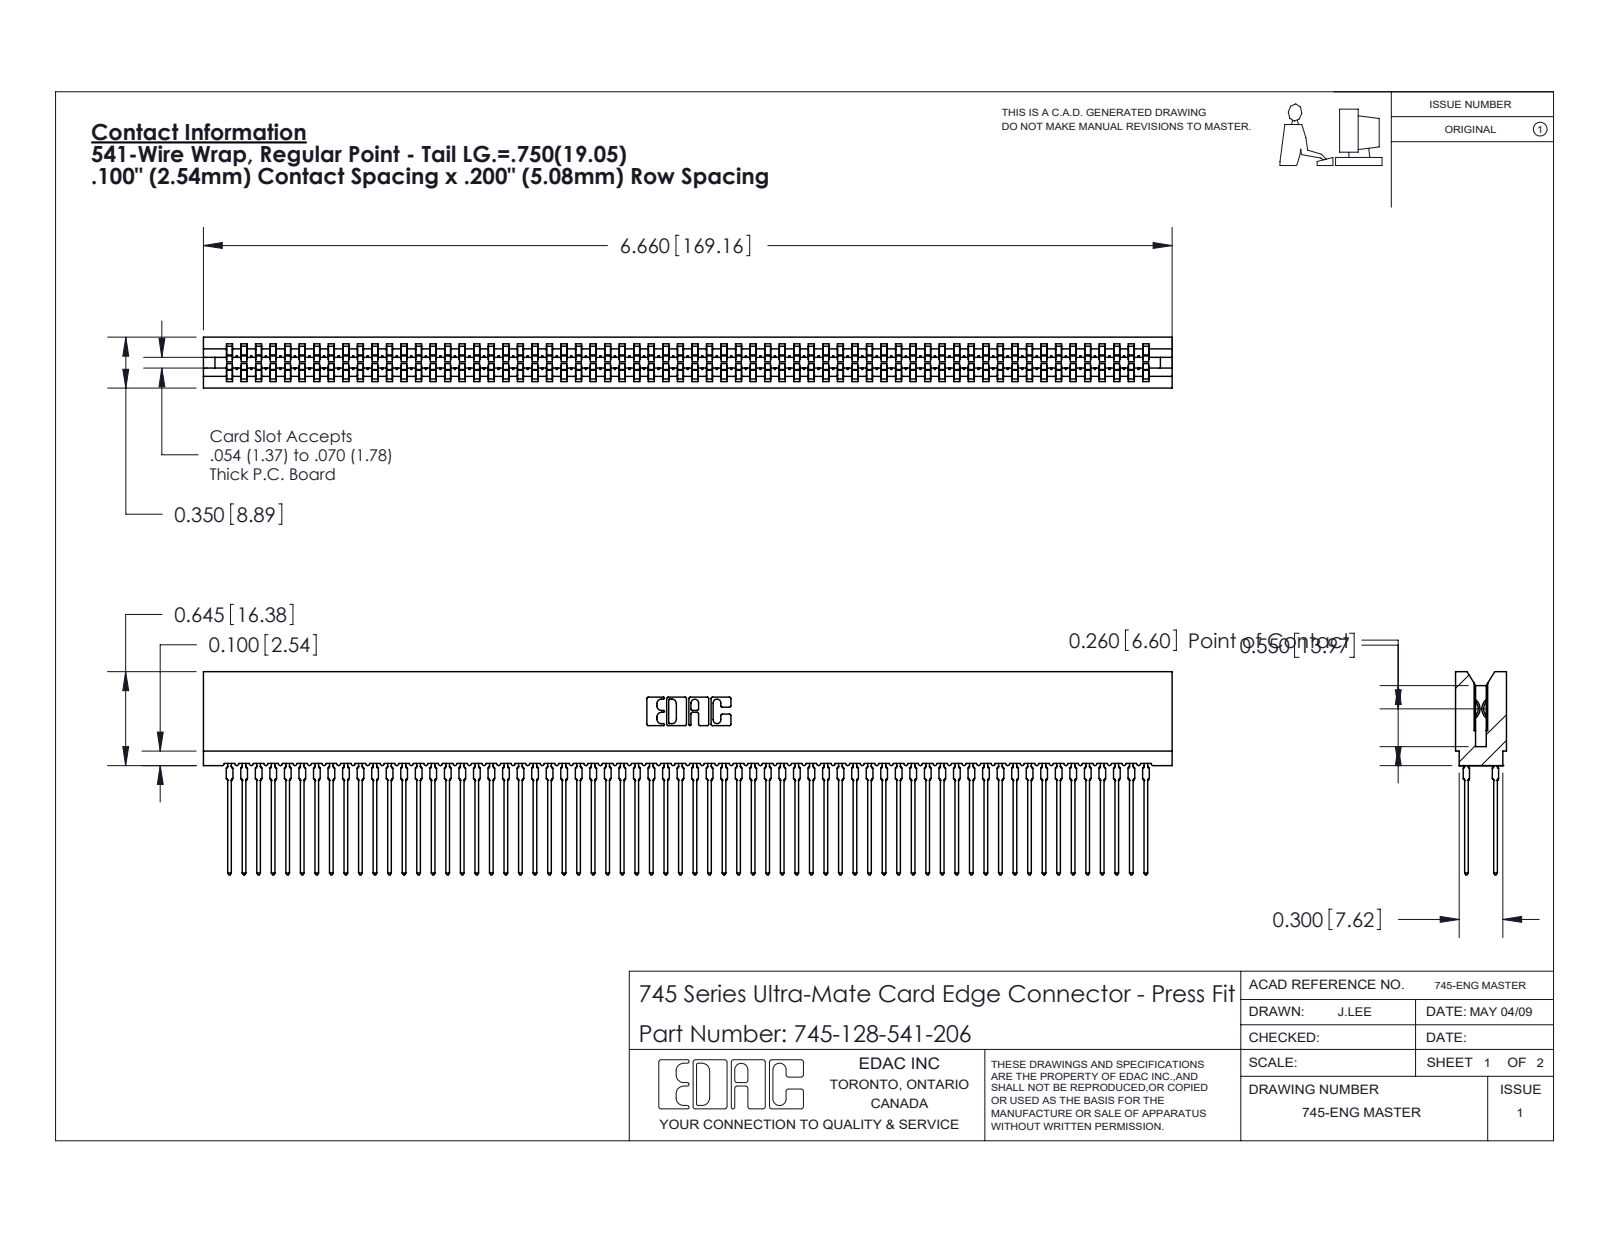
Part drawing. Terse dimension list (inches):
name: 745-292-001_541; 745-128-541-206; 745 Part_Insulator Option - 06
written by: SolidWorks 2020 (CONFIG_CONTROL_DESIGN)
unit: in
bodies: 129 solids, 11552 faces (5944 planar, 2280 cylindrical, 3328 other)
size: 6.66 × 1.396 × 0.35
volume: 0.958 in³; area: 54.26 in²
rounds: 256× R0.021, 128× R0.015, 22× R0.01, 8× R0.005, 8× R0.011, 6× R0.007, 6× R0.031, 3× R0.026
face distances: 0.063, 0.287, 0.2, 0.35, 0.087, 0.263, 0.025, 0.045, 0.305, 0.018
